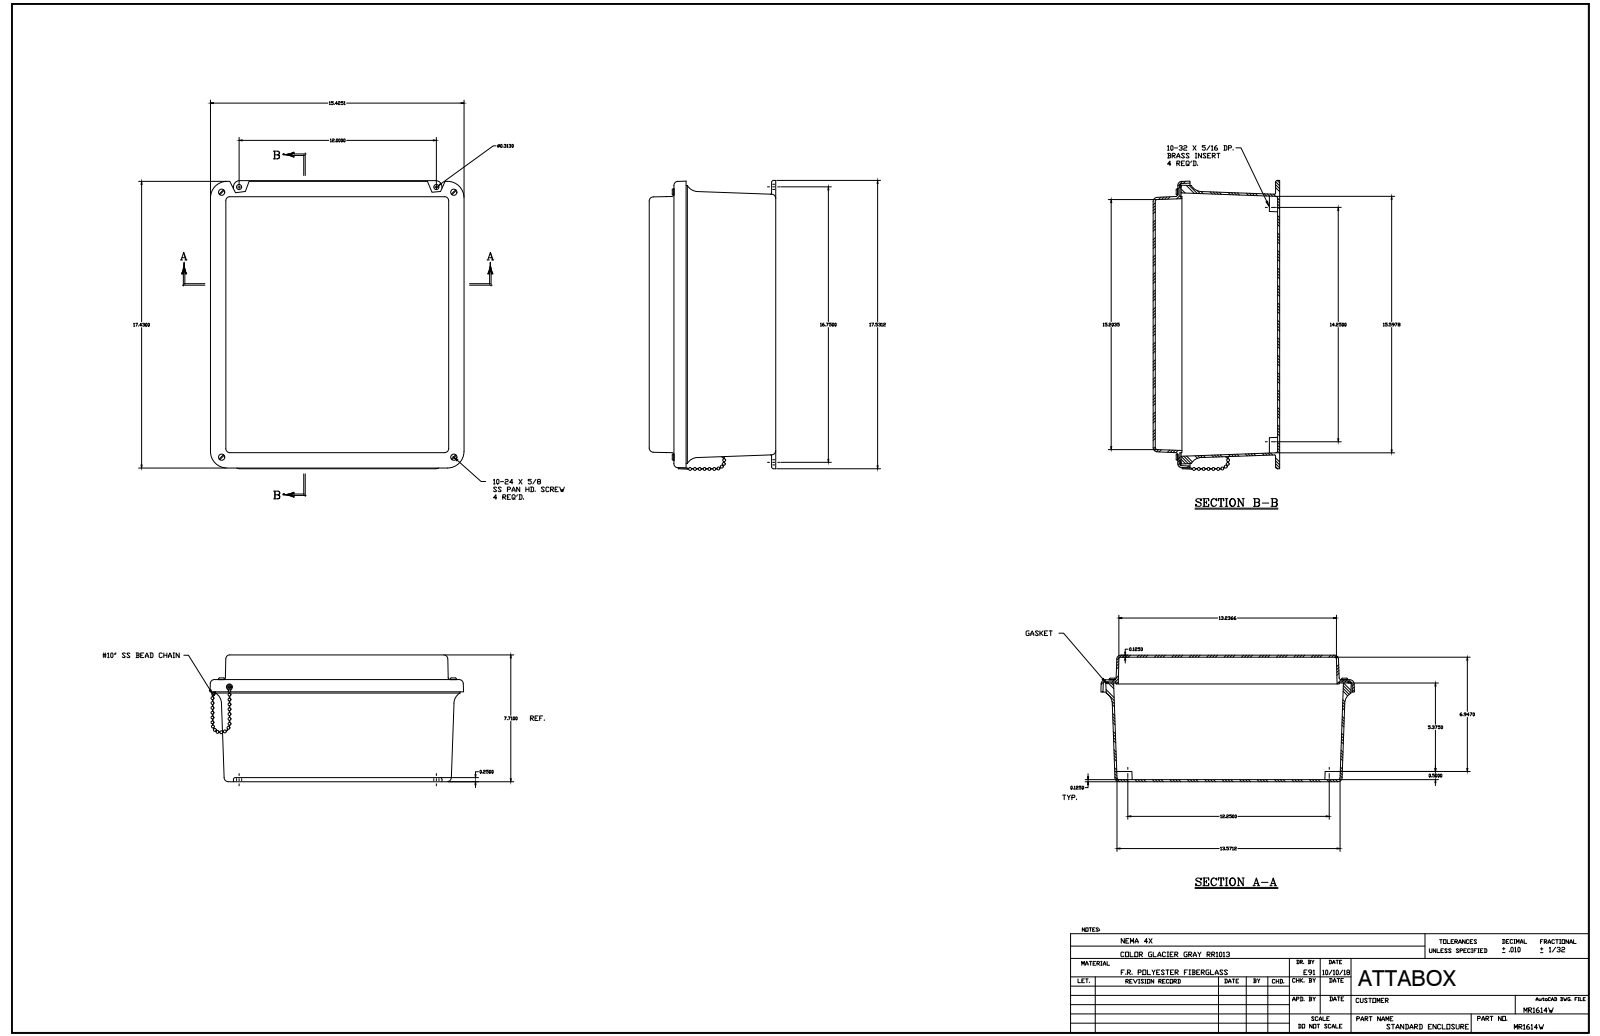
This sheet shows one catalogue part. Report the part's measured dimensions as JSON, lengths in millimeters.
{"part_name": "MR1614W", "step_written_by": "SolidWorks 2018 (AUTOMOTIVE_DESIGN)", "units": "millimeters", "bodies": {"solids": 45, "faces": 949, "planar": 214, "cylindrical": 307, "other": 428}, "overall_size": [457.6, 397.9, 195.2], "volume_mm3": 2393000, "surface_area_mm2": 1327000, "round_holes": [[3.9, 8], [3.6, 6], [3.7, 4], [4, 4], [5.5, 4], [4.7, 2], [3.2, 1]], "round_bosses_or_shafts": [[6.9, 8], [4.8, 4], [4, 4], [6.4, 2], [9.5, 1], [9.5, 1], [7.2, 1], [3.2, 1]], "partial_cylinders_radius": [[0.8, 20], [3.2, 20], [6.4, 20], [5.1, 4], [7.5, 4], [9.5, 4], [19.1, 4], [0.3, 2]], "face_to_face_distances": [3.2, 3.2, 188.8, 195.2, 192, 192, 38.2, 150.7, 153.8, 41.3], "hole_center_spacings": [33.6, 335.8, 386.3, 510.7, 95.3, 190.5, 311.2, 358.8]}
